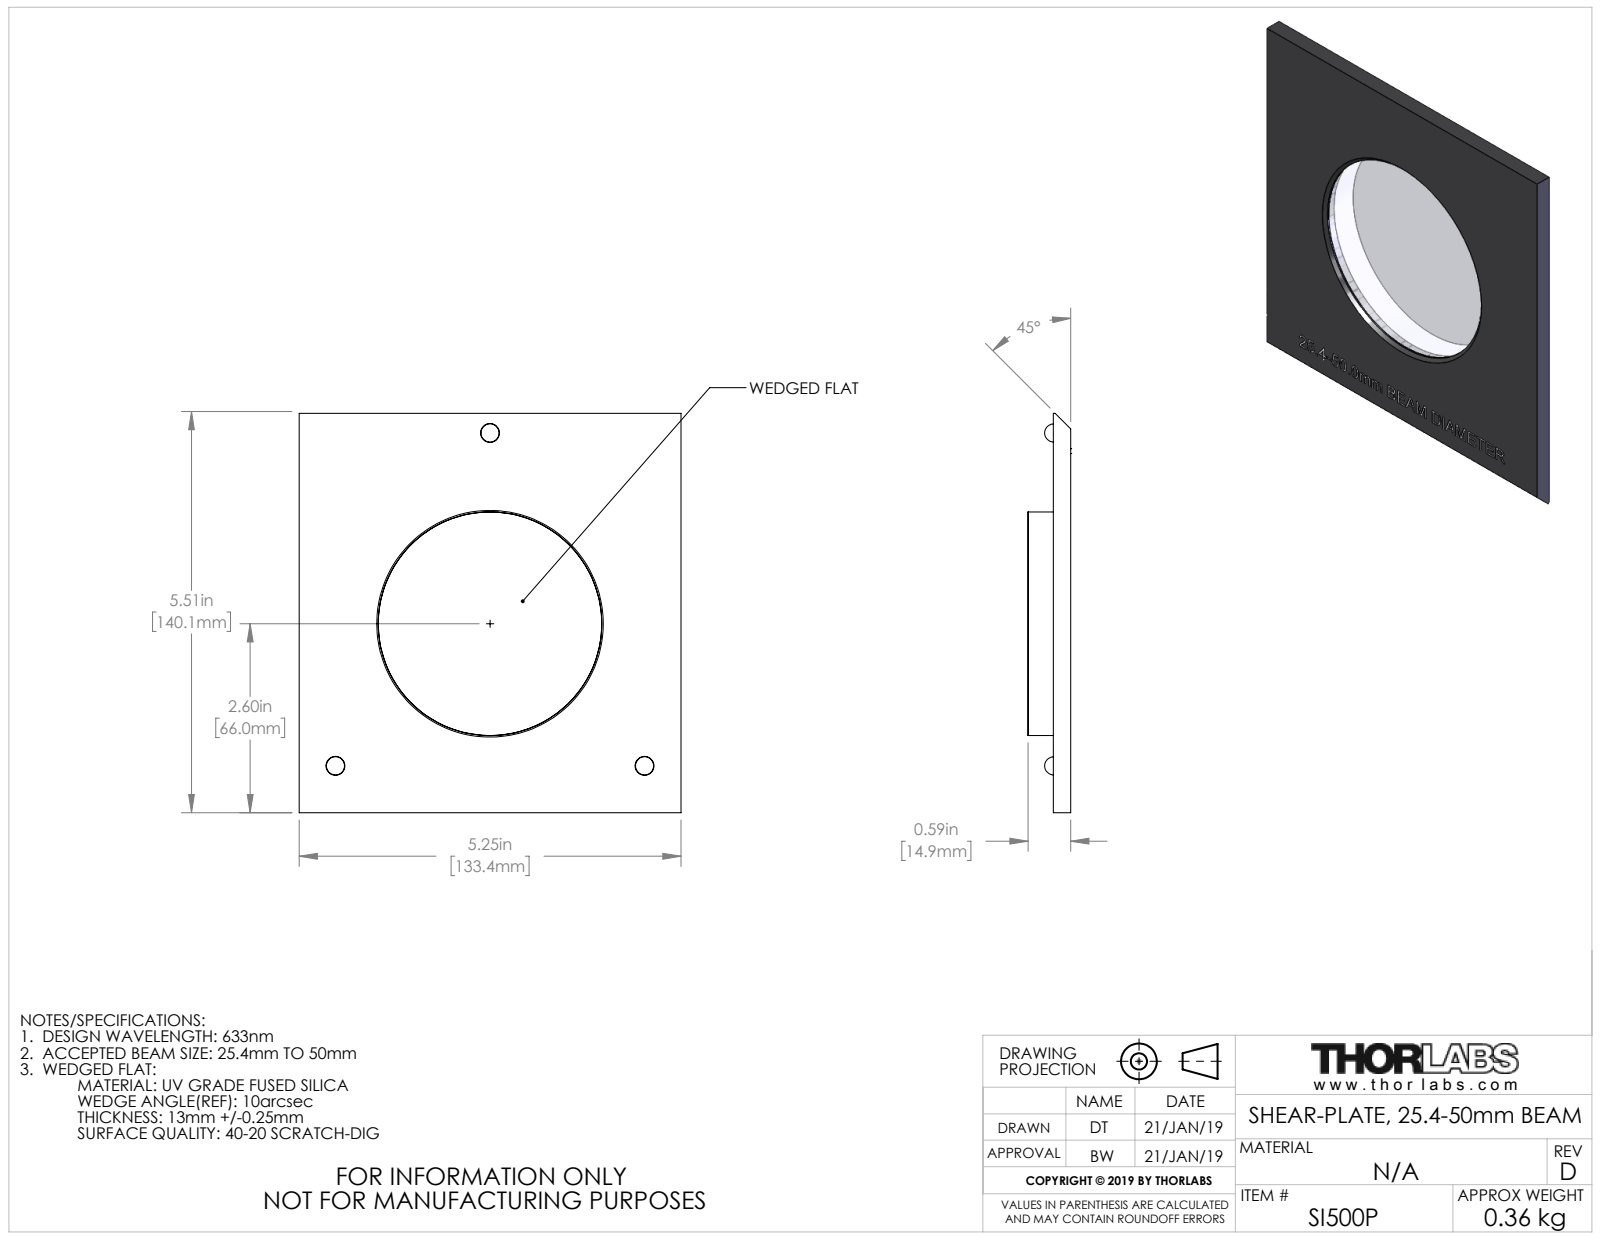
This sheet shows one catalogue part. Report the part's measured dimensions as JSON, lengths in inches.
{"part_name": "16658-E0W", "step_written_by": "SolidWorks 2018 (CONFIG_CONTROL_DESIGN)", "units": "inches", "bodies": {"solids": 5, "faces": 366, "planar": 233, "cylindrical": 12, "other": 121}, "overall_size": [5.489, 5.25, 0.588], "volume_in3": 8.785, "surface_area_in2": 70.52, "round_holes": [[0.249, 3], [2.991, 1], [3.074, 1]], "round_bosses_or_shafts": [[3.071, 1]], "face_to_face_distances": [0.238, 0.076, 0.162, 0.512, 0.588, 0.35, 5.25, 0.075, 0.237, 0.587], "hole_center_spacings": [2.622, 2.886, 2.886, 4.25, 5.044, 5.044]}
